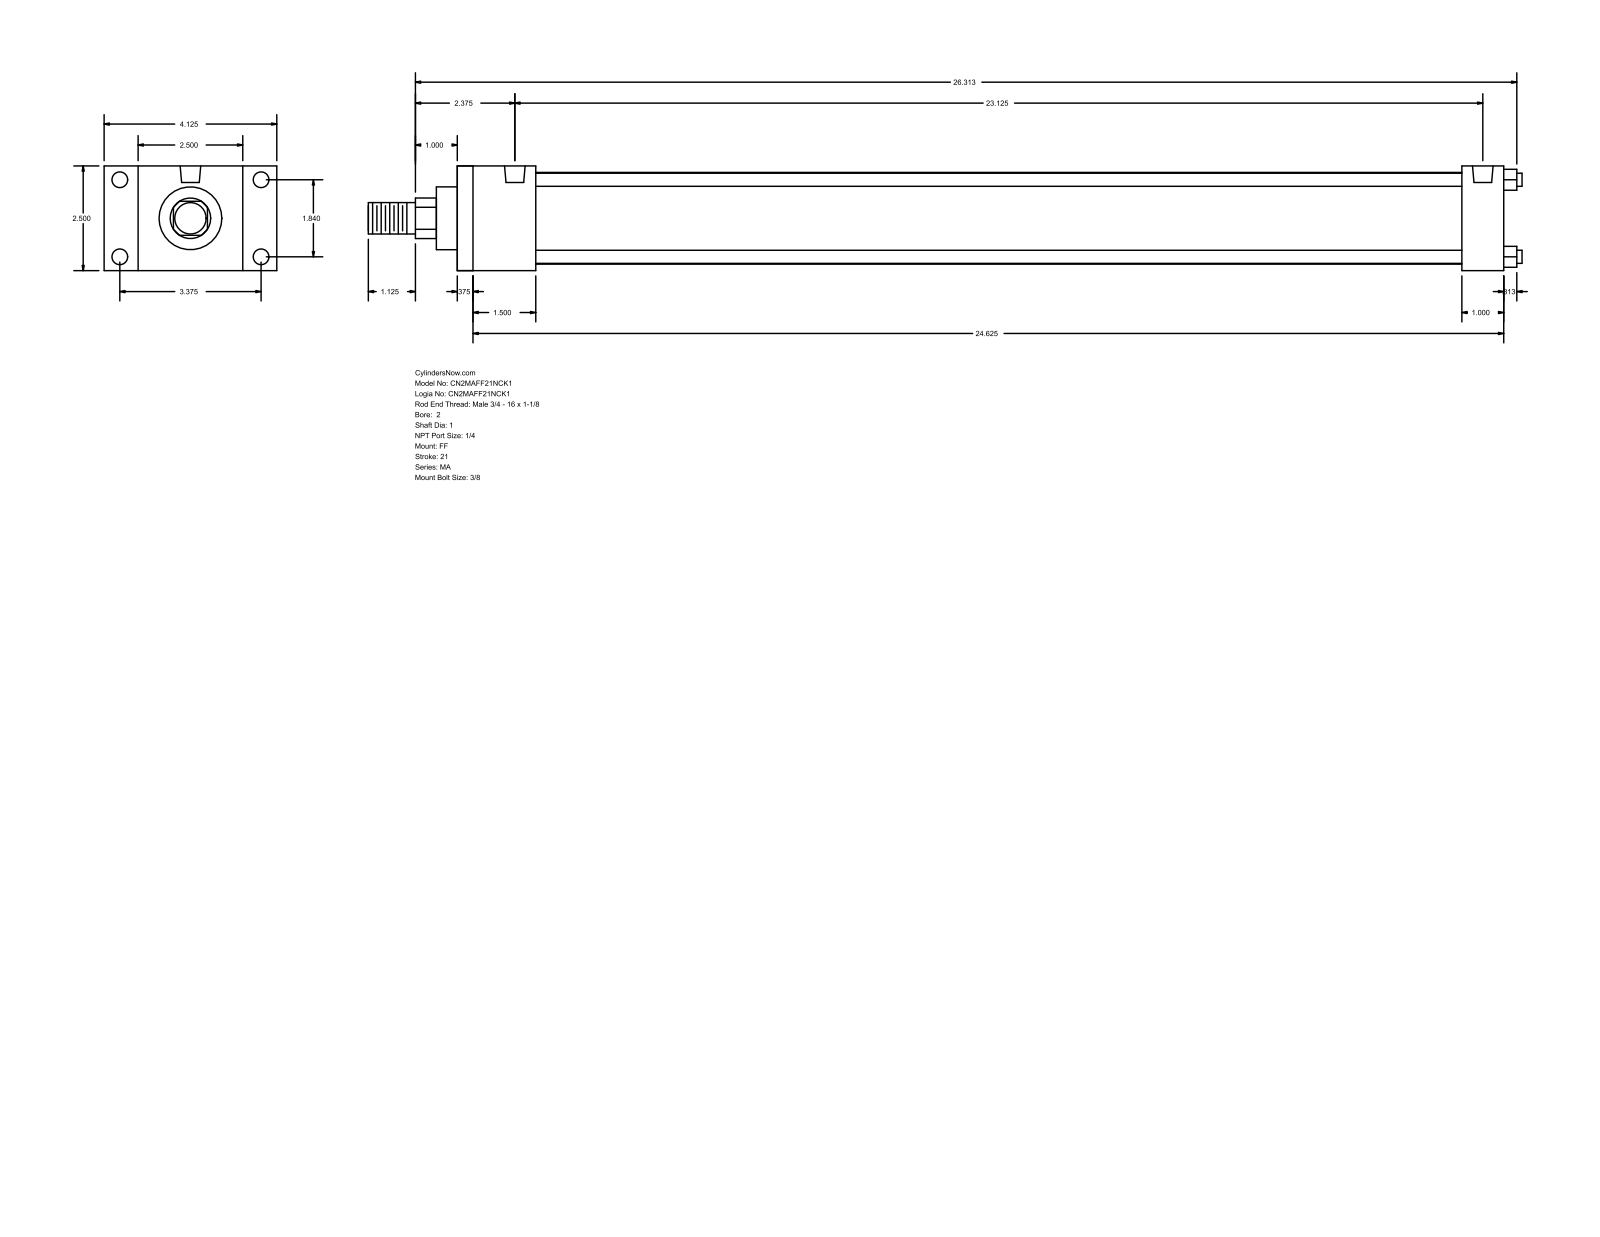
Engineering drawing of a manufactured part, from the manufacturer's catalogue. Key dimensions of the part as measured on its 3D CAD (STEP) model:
Part name (STEP PRODUCT): MA_FF__0200_1
STEP written by: GSSL Pune (CONFIG_CONTROL_DESIGN)
Units: millimetres
Bodies: 0 solids, 92 faces (64 planar, 28 cylindrical, 0 other)
Overall size (bounding box): 700.09 × 104.78 × 63.5
Round holes (diameter × count): ⌀7.94 ×4, ⌀9.53 ×4, ⌀12.49 ×2
Round bosses / shafts (diameter × count): ⌀7.94 ×4, ⌀55.63 ×1, ⌀38.1 ×1, ⌀25.4 ×1, ⌀19.05 ×1
Partial cylindrical surfaces — rounded edges, fillets, slot ends (radius × count): R12.29 ×1
Main face-to-face distances: 63.5, 635, 9.52, 625.48, 25.4, 20.64, 12.7, 47.63, 609.6, 38.11
Hole centre spacings: 46.74, 85.72, 97.63, 587.37
